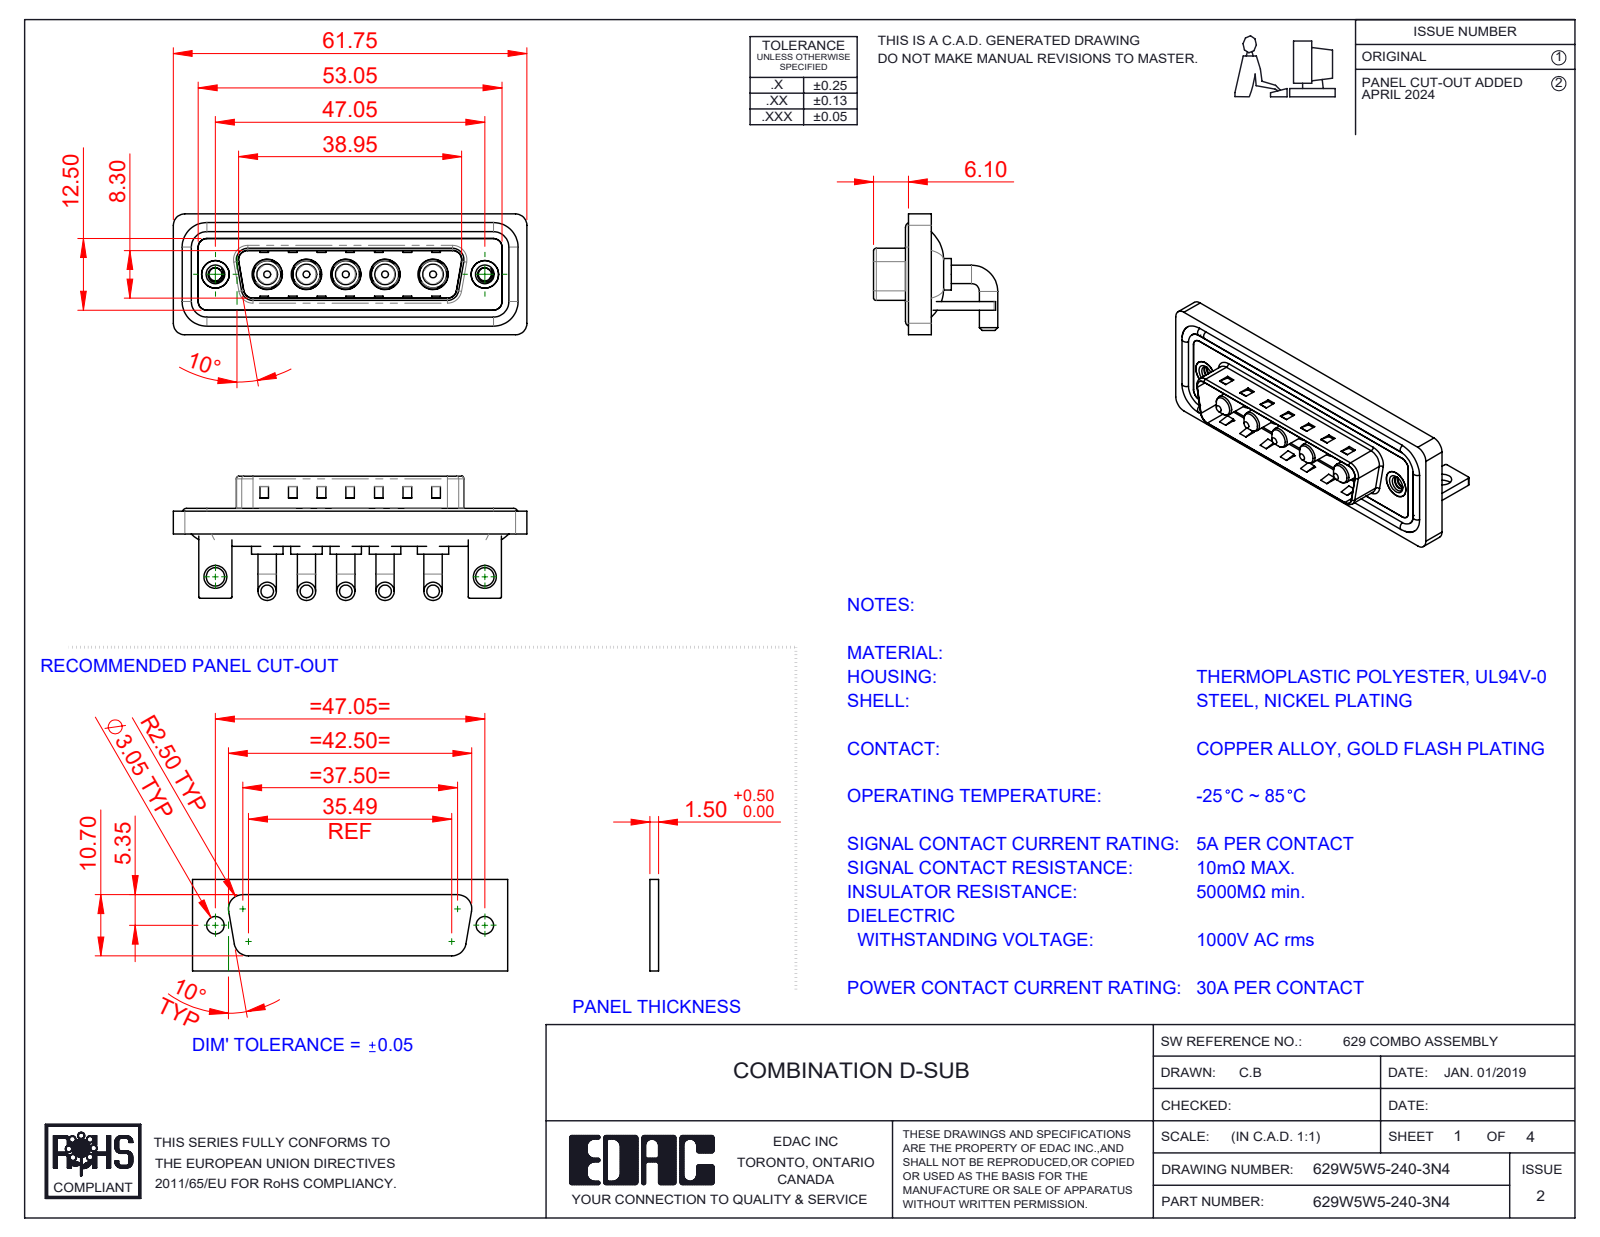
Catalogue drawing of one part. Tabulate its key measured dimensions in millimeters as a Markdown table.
| quantity | value |
| --- | --- |
| part name | 629Combo Threaded Rivet_3; 629Combo Shell Front_25 Contacts; 629Combo Stabilizer Bracket; Power Pin_30A RA (+4 more) |
| STEP written by | SolidWorks 2023 (CONFIG_CONTROL_DESIGN) |
| units | millimeters |
| bodies | 19 solids, 738 faces (279 planar, 311 cylindrical, 148 other) |
| overall size | 61.75 × 21.7 × 21.1 |
| volume | 8 220 mm³ |
| surface area | 12 951 mm² |
| round holes (diameter × count) | 4.85 × 5, 5.3 × 5, 2.26 × 2, 3.2 × 2, 4 × 2, 4.8 × 2, 5 × 2 |
| round bosses / shafts (diameter × count) | 3.2 × 10, 5.5 × 5, 5.2 × 5, 4.75 × 5, 3.75 × 5, 3.6 × 5, 1.6 × 4, 4.9 × 2 |
| partial cylindrical surfaces (radius × count) | 2 × 19, 1.5 × 18, 0.25 × 16, 0.5 × 9, 1.6 × 8, 2.1 × 5, 0.6 × 4, 0.65 × 4 |
| main face-to-face distances | 0.4, 1.5, 2.9, 0.8, 2.1, 1.1, 3.7, 4.5, 4.1, 1.2 |
| hole center spacings | 6.86, 13.73, 47.05, 6.85, 6.87, 8.37, 8.38, 9.04 |
